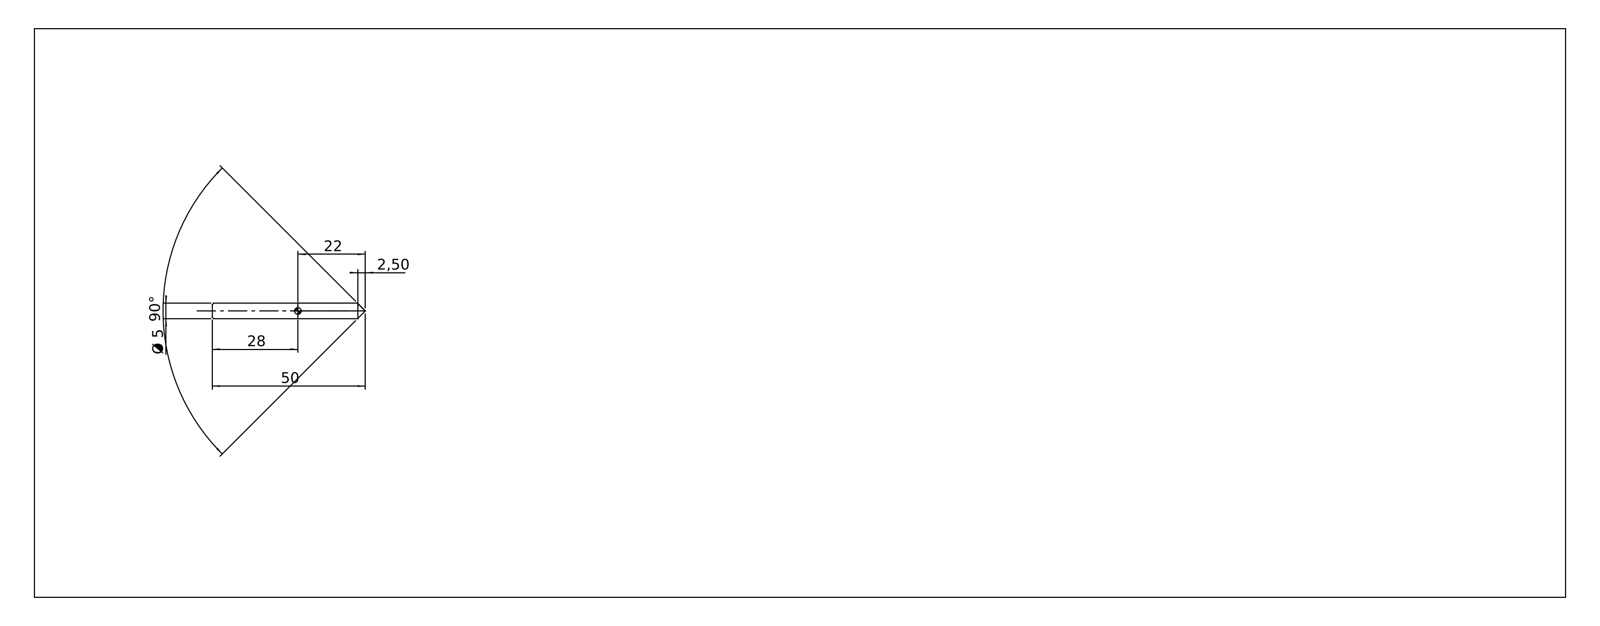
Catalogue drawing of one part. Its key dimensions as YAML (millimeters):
part_name: "890.050.00"
step_written_by: "SolidWorks 2019 (CONFIG_CONTROL_DESIGN)"
units: millimeters
bodies: {solids: 2, faces: 6, planar: 3, cylindrical: 1, other: 2}
overall_size: [50, 5, 5]
volume: 947
surface_area: 828
round_bosses_or_shafts:
  - {diameter: 5, count: 1}
face_to_face_distances: [47.5]
